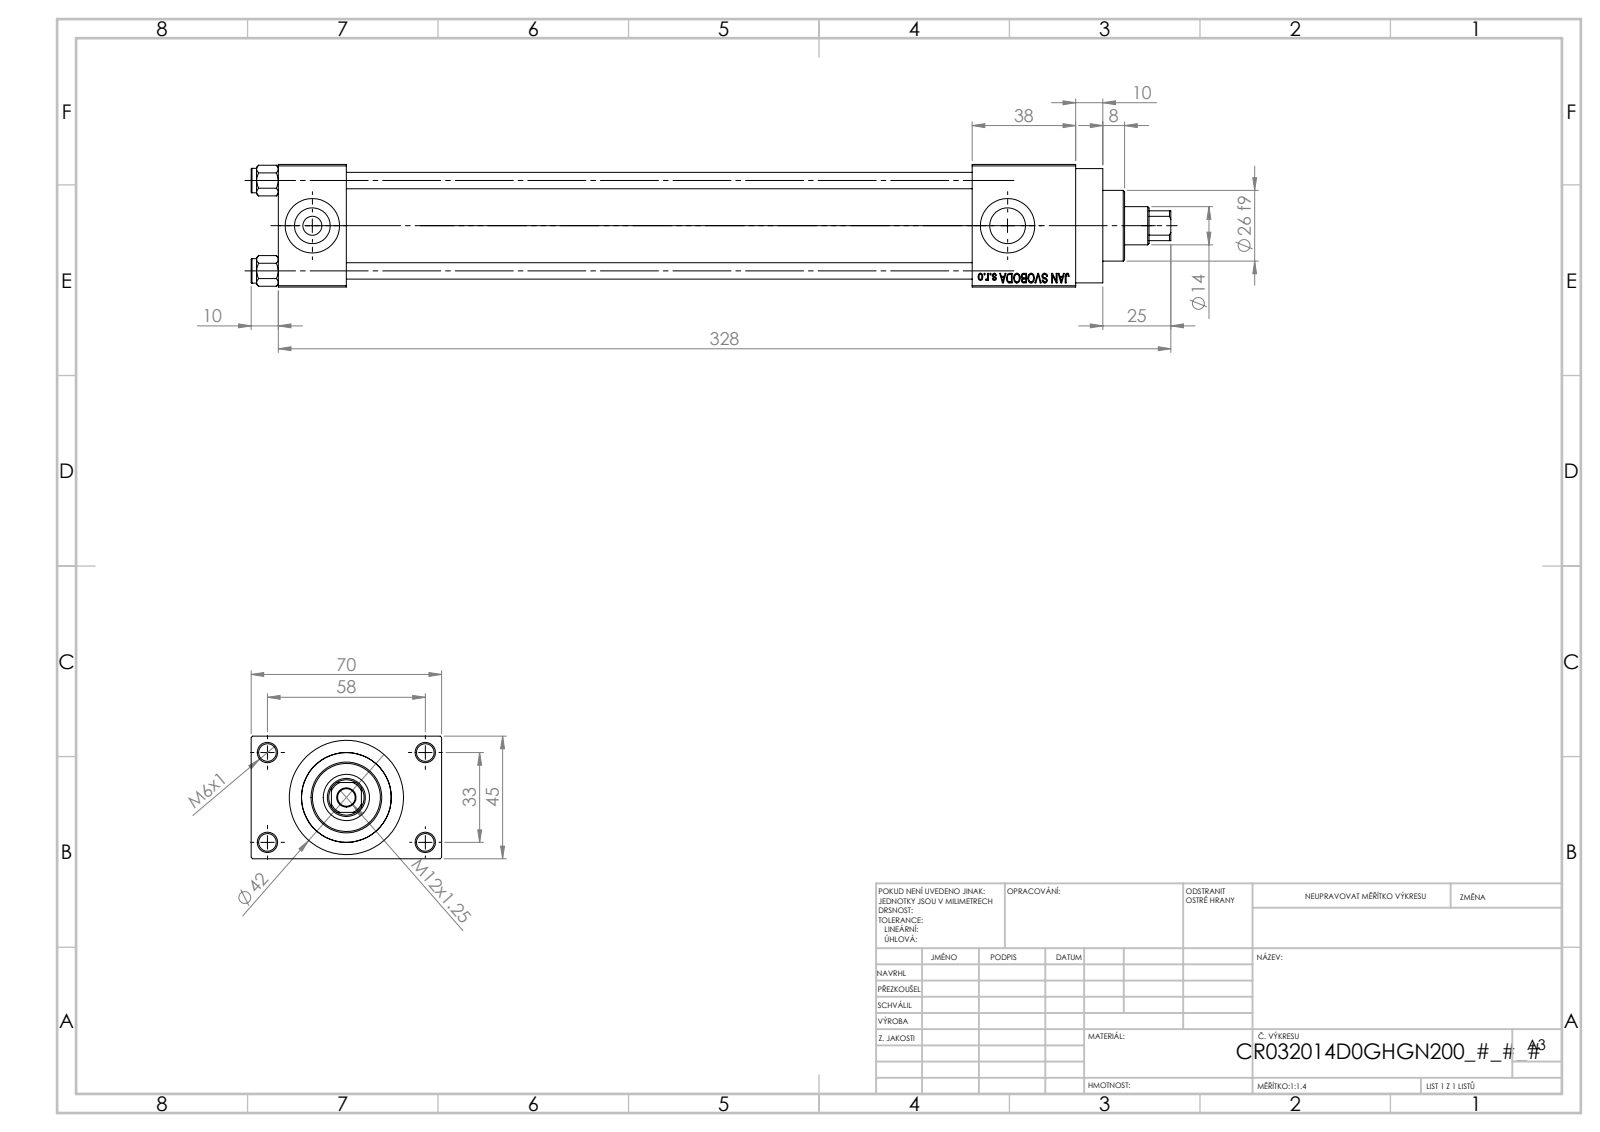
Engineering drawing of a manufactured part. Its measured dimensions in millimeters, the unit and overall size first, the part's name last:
Units: millimetres
Overall size (bounding box): 338 × 70 × 45
Round holes (diameter × count): ⌀6.5 ×5, ⌀6 ×4, ⌀7 ×2, ⌀13.16 ×2, ⌀20 ×2, ⌀14 ×1, ⌀17 ×1, ⌀24 ×1, ⌀32 ×1, ⌀33 ×1
Round bosses / shafts (diameter × count): ⌀9 ×4, ⌀42 ×1, ⌀38 ×1, ⌀26 ×1
Partial cylindrical surfaces — rounded edges, fillets, slot ends (radius × count): R6.5 ×1
Main face-to-face distances: 45, 25, 12.5, 230, 255, 57.5, 268, 38, 293, 70
Hole centre spacings: 12.4, 23.48, 33.2, 33.37, 35.35, 45.6, 56.35, 33
Volume: 337 769 mm³ · Surface area: 136 461 mm²
Bodies: 11 solids, 1102 faces (496 planar, 88 cylindrical, 518 other)
Part name (STEP PRODUCT): NUT_M5_D; V215CR_D_TYCINKA; V215_VC_A; V215CR_VCP_D (+1 more)
STEP written by: SolidWorks 2019 (CONFIG_CONTROL_DESIGN)
